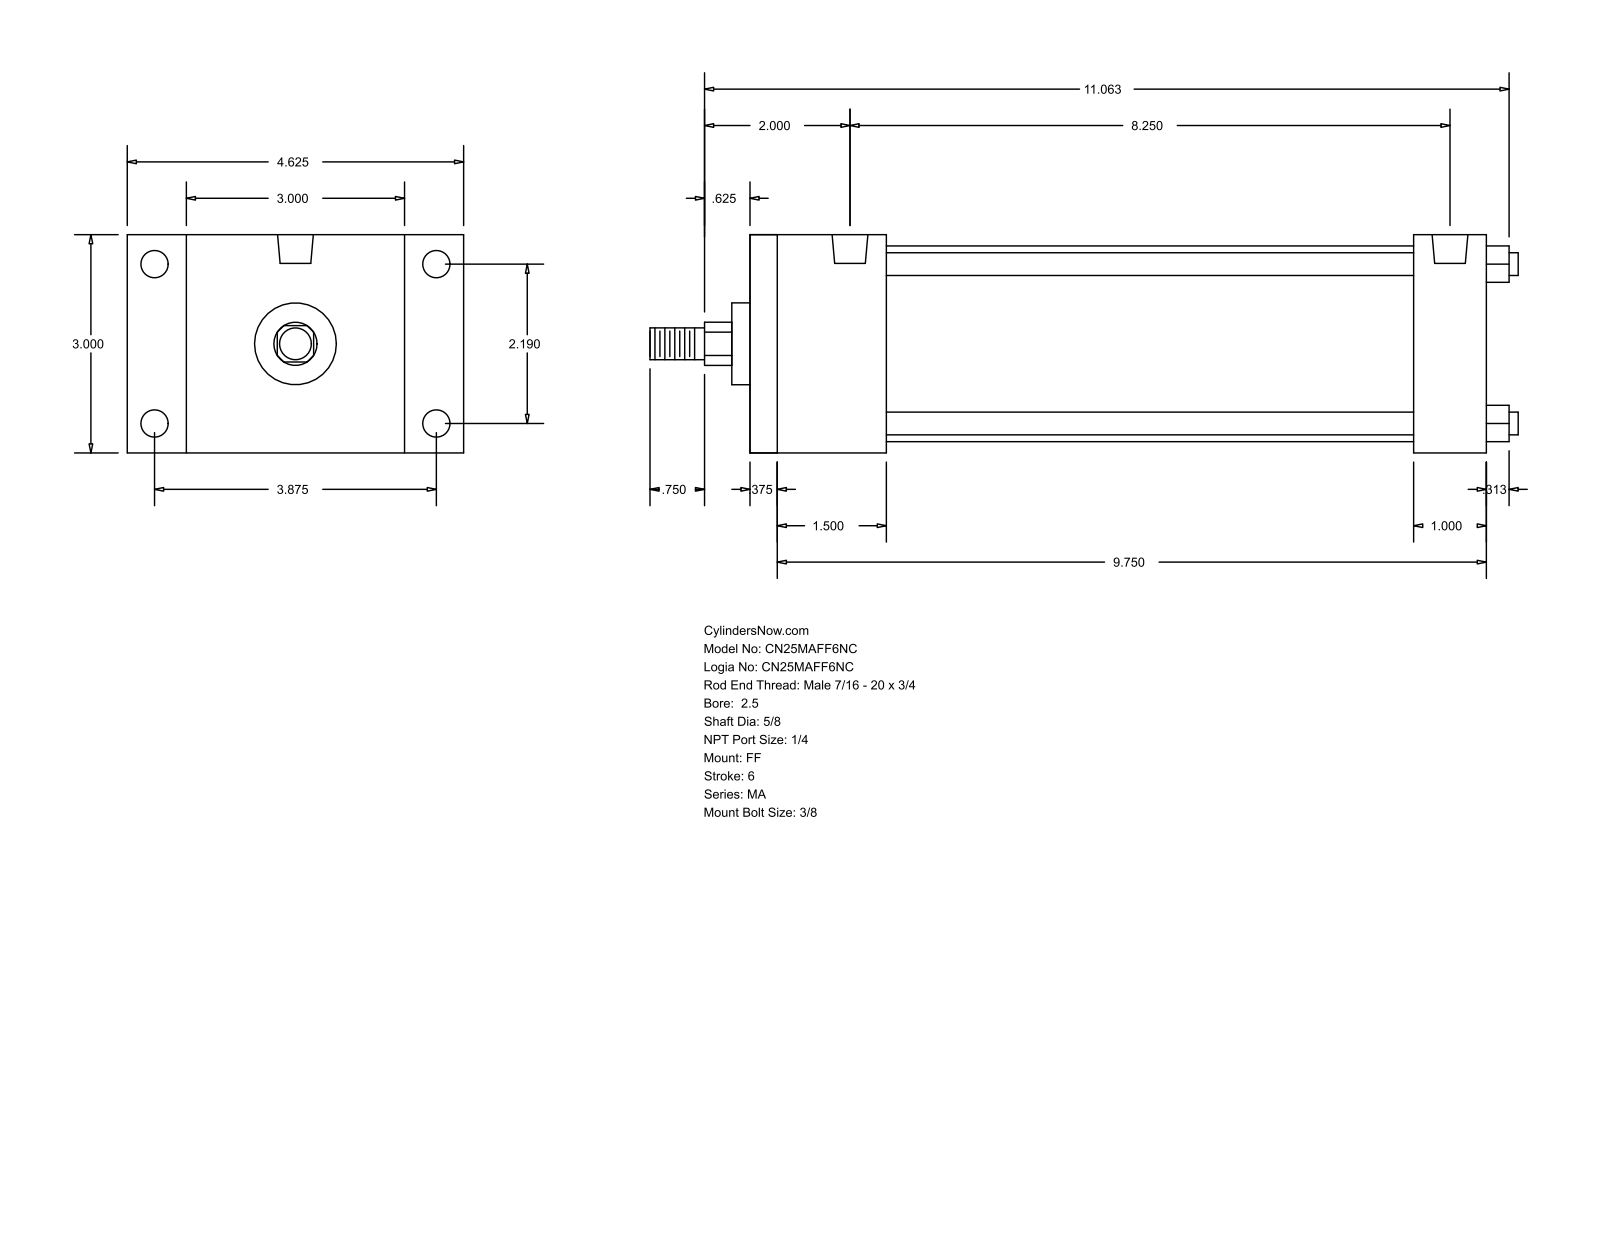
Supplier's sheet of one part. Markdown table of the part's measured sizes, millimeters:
| quantity | value |
| --- | --- |
| part name | MA_FF__0250_0.625 |
| STEP written by | GSSL Pune (CONFIG_CONTROL_DESIGN) |
| units | millimeters |
| bodies | 0 solids, 92 faces (64 planar, 28 cylindrical, 0 other) |
| overall size | 303.21 × 117.47 × 76.2 |
| round holes (diameter × count) | 7.94 × 4, 9.53 × 4, 12.49 × 2 |
| round bosses / shafts (diameter × count) | 7.94 × 4, 68.33 × 1, 28.57 × 1, 15.88 × 1, 11.11 × 1 |
| partial cylindrical surfaces (radius × count) | 7.54 × 1 |
| main face-to-face distances | 76.2, 257.17, 247.65, 9.52, 25.4, 47.62, 231.77, 38.1, 222.25, 184.15 |
| hole center spacings | 55.62, 98.42, 113.05, 209.55 |
